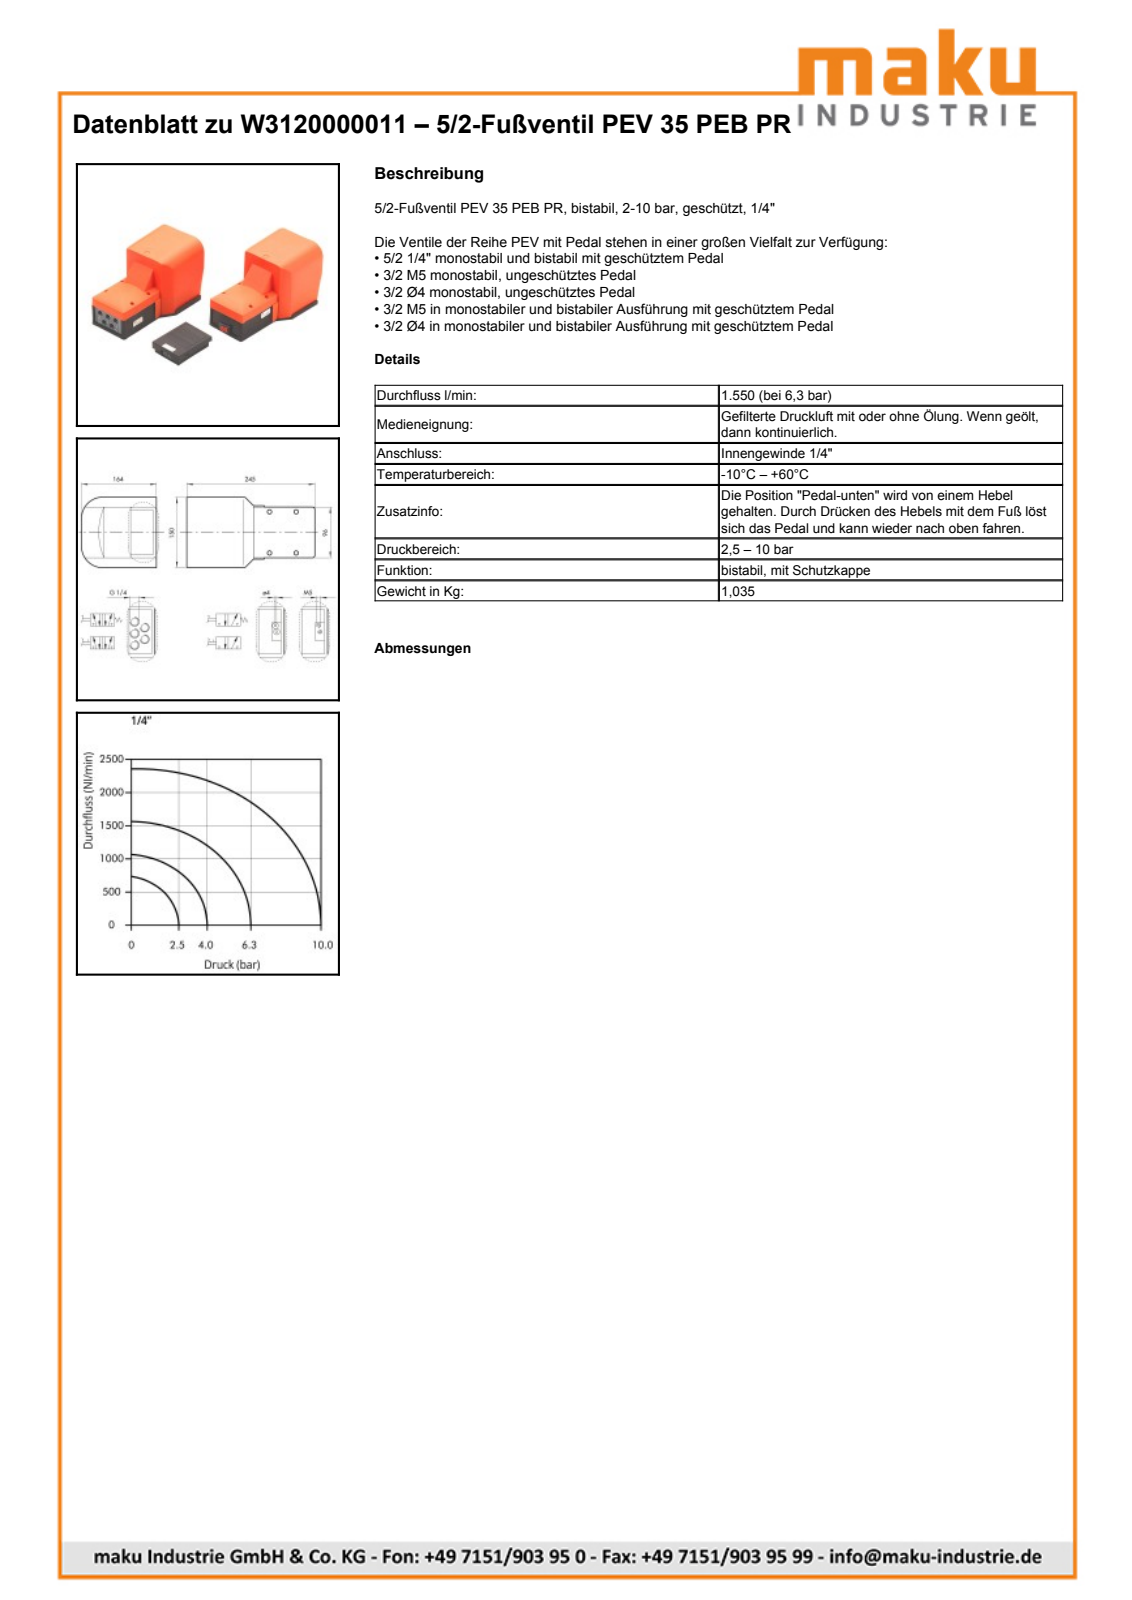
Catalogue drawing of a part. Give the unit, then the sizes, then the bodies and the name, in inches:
Units: inches
Overall size (bounding box): 9.547 × 6.457 × 5.906
Round holes (diameter × count): ⌀0.451 ×5, ⌀0.157 ×4, ⌀0.315 ×1, ⌀1.102 ×1
Round bosses / shafts (diameter × count): ⌀0.512 ×4, ⌀0.354 ×4, ⌀0.315 ×4, ⌀0.276 ×4, ⌀0.394 ×2, ⌀1.417 ×1, ⌀0.866 ×1, ⌀0.165 ×1
Partial cylindrical surfaces — rounded edges, fillets, slot ends (radius × count): R0.157 ×4, R0.236 ×3, R0.059 ×2, R0.886 ×2, R0.984 ×2, R0.3 ×1
Main face-to-face distances: 0.098, 0.276, 5.61, 4.646, 0.965, 4.744, 0.866, 1.063, 5.709, 4.547
Hole centre spacings: 0.864, 0.874, 0.886, 1.516, 2.008, 3.15, 3.251, 3.735
Volume: 38.1 in³ · Surface area: 489.8 in²
Bodies: 8 solids, 465 faces (356 planar, 78 cylindrical, 31 other)
Part name (STEP PRODUCT): W3120000011(3BPR); W3120000011Pedal; W3120000011Body; W3120000011Body1 (+2 more)
STEP written by: PARTsolutions (AUTOMOTIVE_DESIGN)
